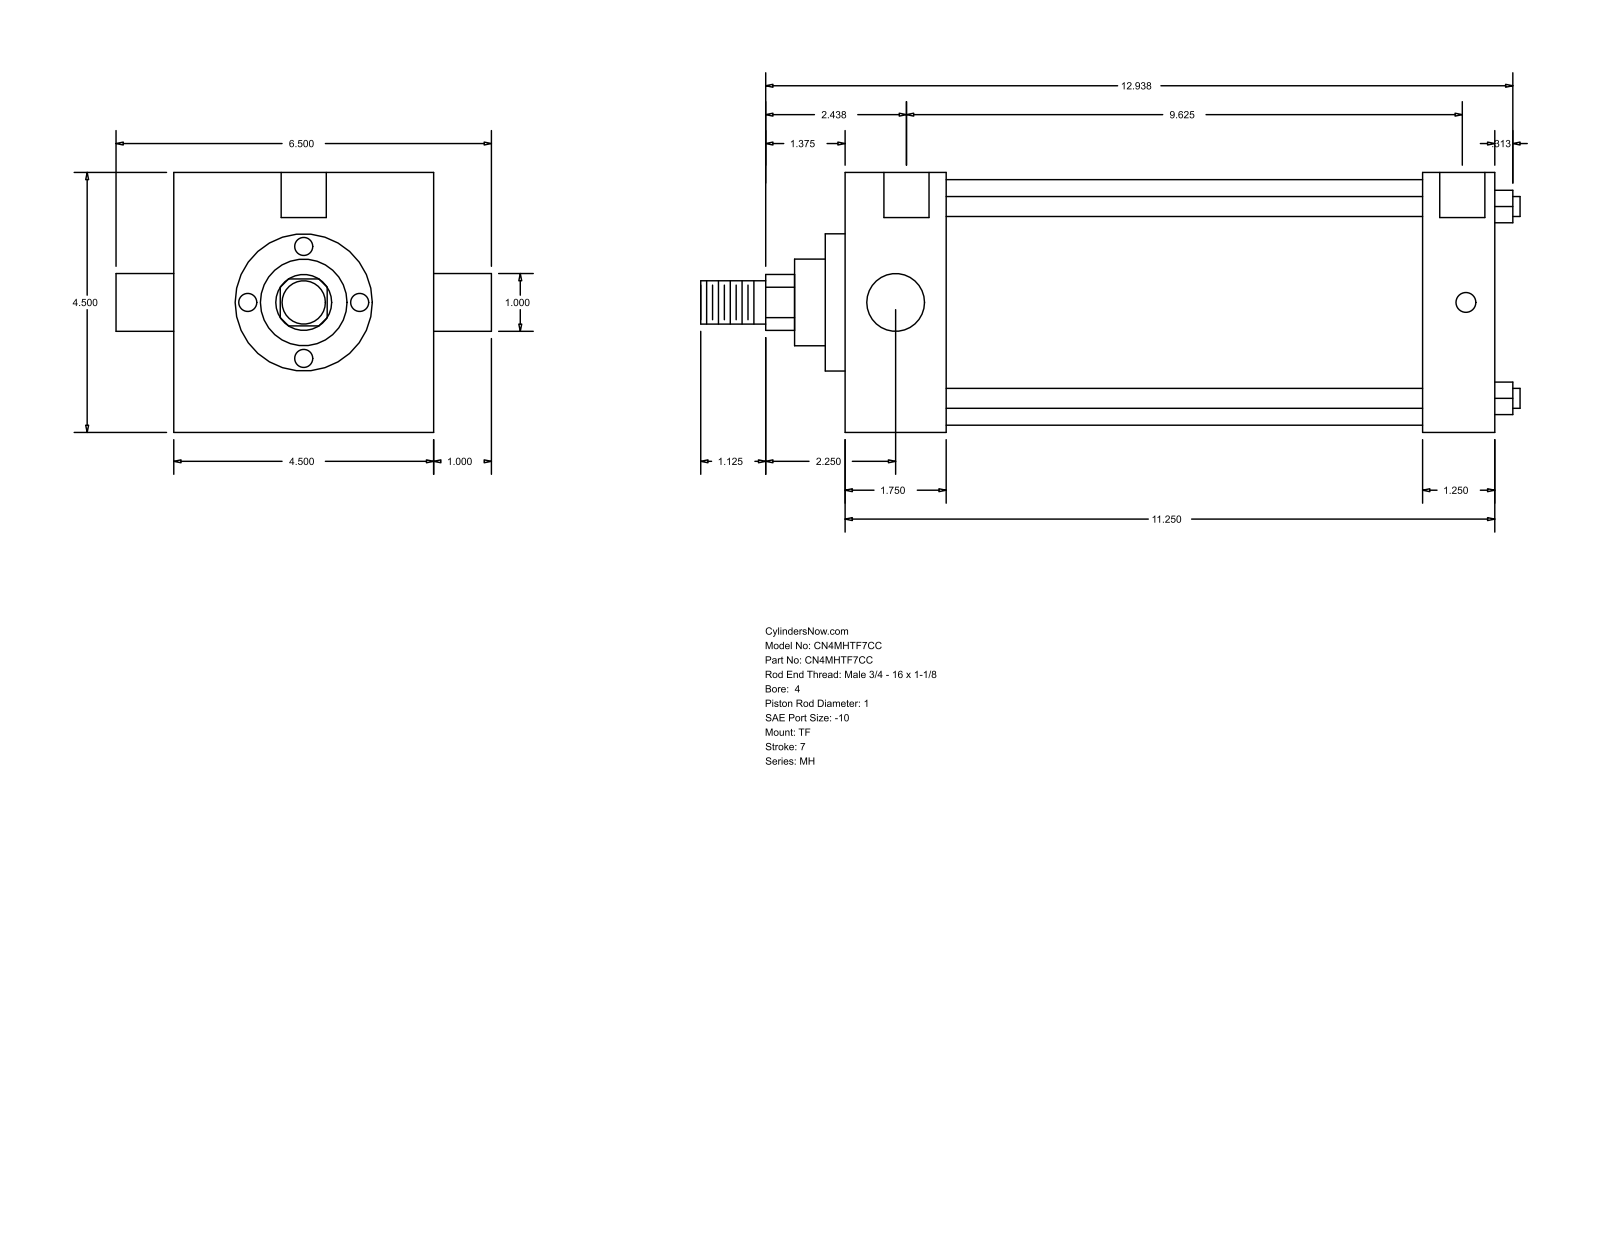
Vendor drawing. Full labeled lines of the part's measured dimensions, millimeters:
Part name (STEP PRODUCT): MH_TF__0400_1
STEP written by: GSSL Pune (CONFIG_CONTROL_DESIGN)
Units: millimetres
Bodies: 0 solids, 86 faces (61 planar, 25 cylindrical, 0 other)
Overall size (bounding box): 360.36 × 165.1 × 114.3
Round holes (diameter × count): ⌀8.73 ×3, ⌀19.84 ×2
Round bosses / shafts (diameter × count): ⌀8.76 ×4, ⌀25.4 ×2, ⌀107.95 ×1, ⌀60.33 ×1, ⌀38.1 ×1, ⌀19.05 ×1
Partial cylindrical surfaces — rounded edges, fillets, slot ends (radius × count): R12.29 ×1
Main face-to-face distances: 114.3, 285.76, 44.46, 241.3, 254.01, 209.55, 31.75, 8.73, 53.19, 262.74
Hole centre spacings: 1.58, 1.59, 244.48, 246.06, 246.07, 247.65
